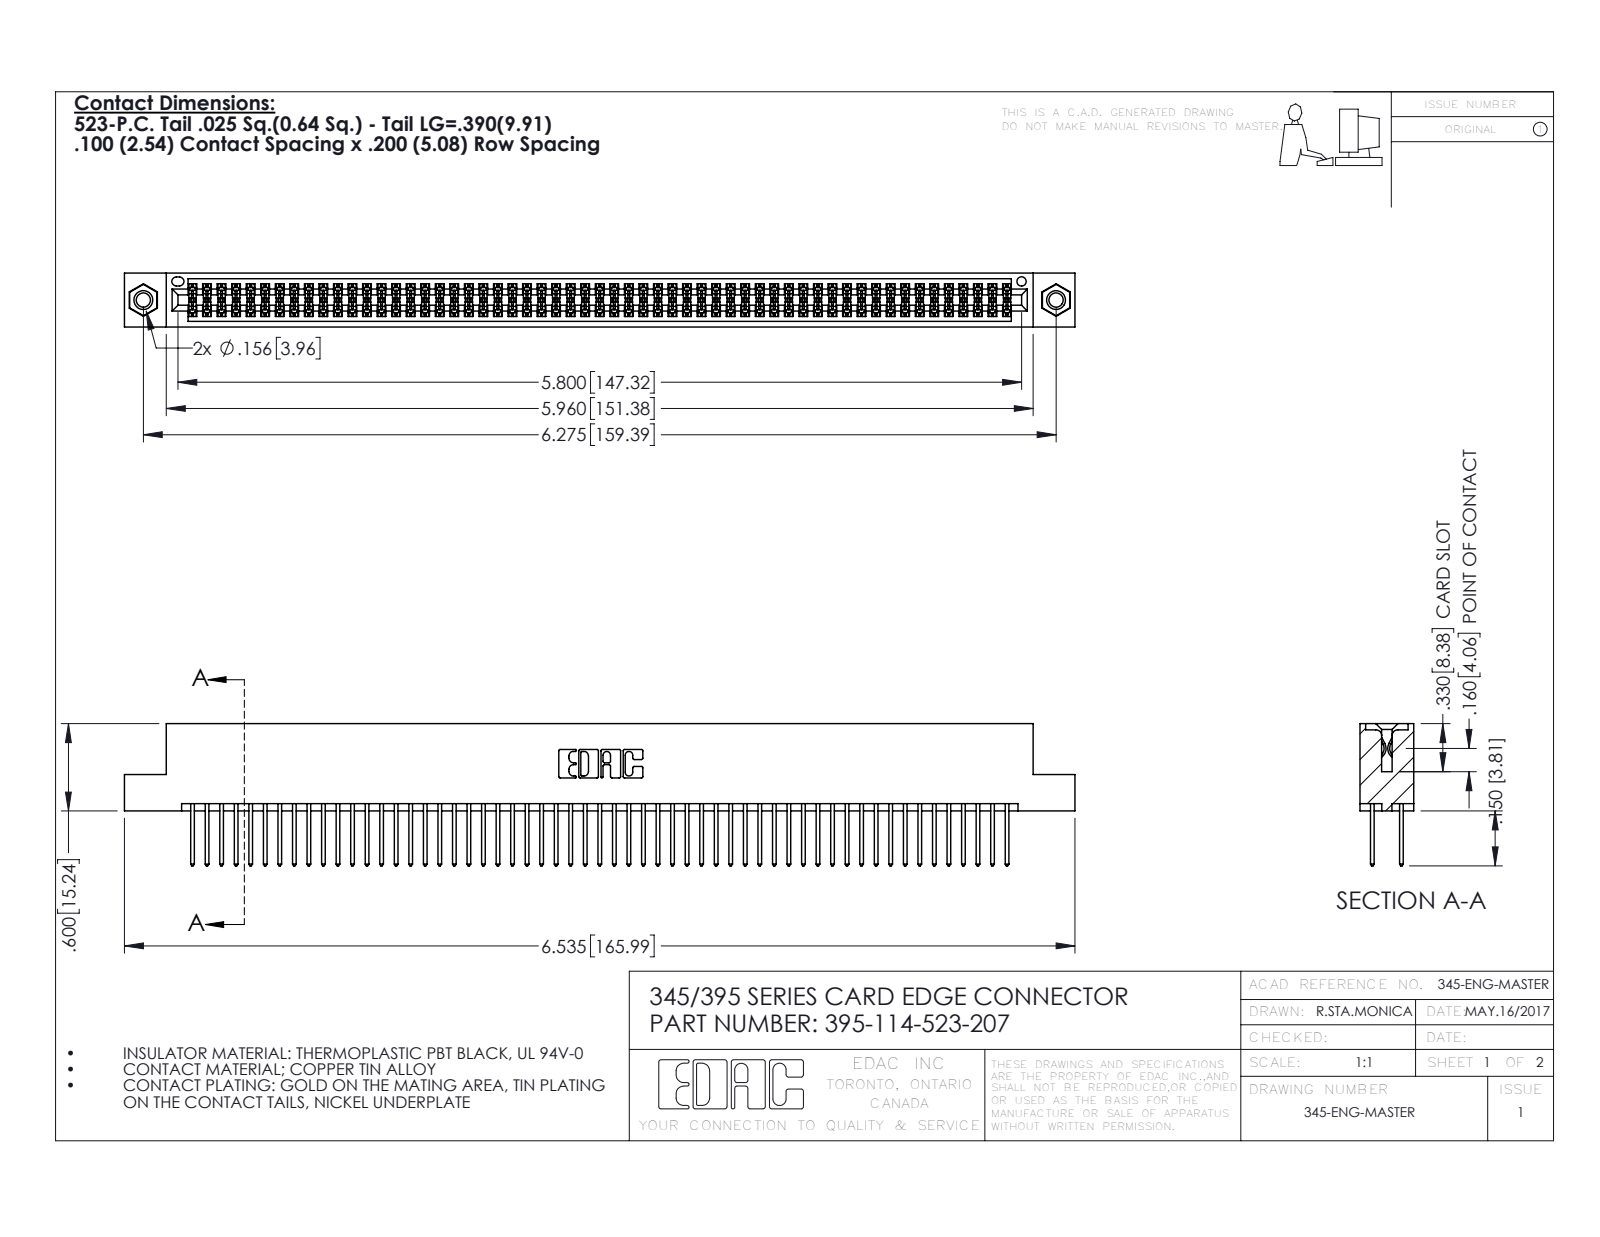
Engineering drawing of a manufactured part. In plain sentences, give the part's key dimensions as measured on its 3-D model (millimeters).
The part is named "345-250-001_345-250-005-103; 345 Part_Flush Mounting Lugs - 0.156 Dia-TI; 345-292-001_345-293-123; 395-114-523-207". Its 3-D file was written by "SolidWorks 2016 (CONFIG_CONTROL_DESIGN)". It is 117 solids with 5886 faces: 3874 planar, 1996 cylindrical and 16 other. Overall it measures 166 by 24.8 by 9.4 millimeters. Its volume is 16 490 cubic millimeters and its surface area 25 740 square millimeters. Round holes: 2 of diameter 2.5, 2 of diameter 3.2, 2 of diameter 4, 1 of diameter 1.6. Round bosses or shafts: 2 of diameter 3.9. Partial cylindrical surfaces (rounded edges, fillets, slot ends): 171 of radius 0.2, 114 of radius 0.3, 22 of radius 0.3, 6 of radius 0.2, 6 of radius 0.8, 3 of radius 0.7, 2 of radius 0.4, 2 of radius 0.5. The main face-to-face distances are 1.8, 7.6, 5.1, 2.5, 6.9, 0.6, 9.4, 5.7, 4.4, 3.8. The hole center spacings are 6.9, 153.4, 159.4.
